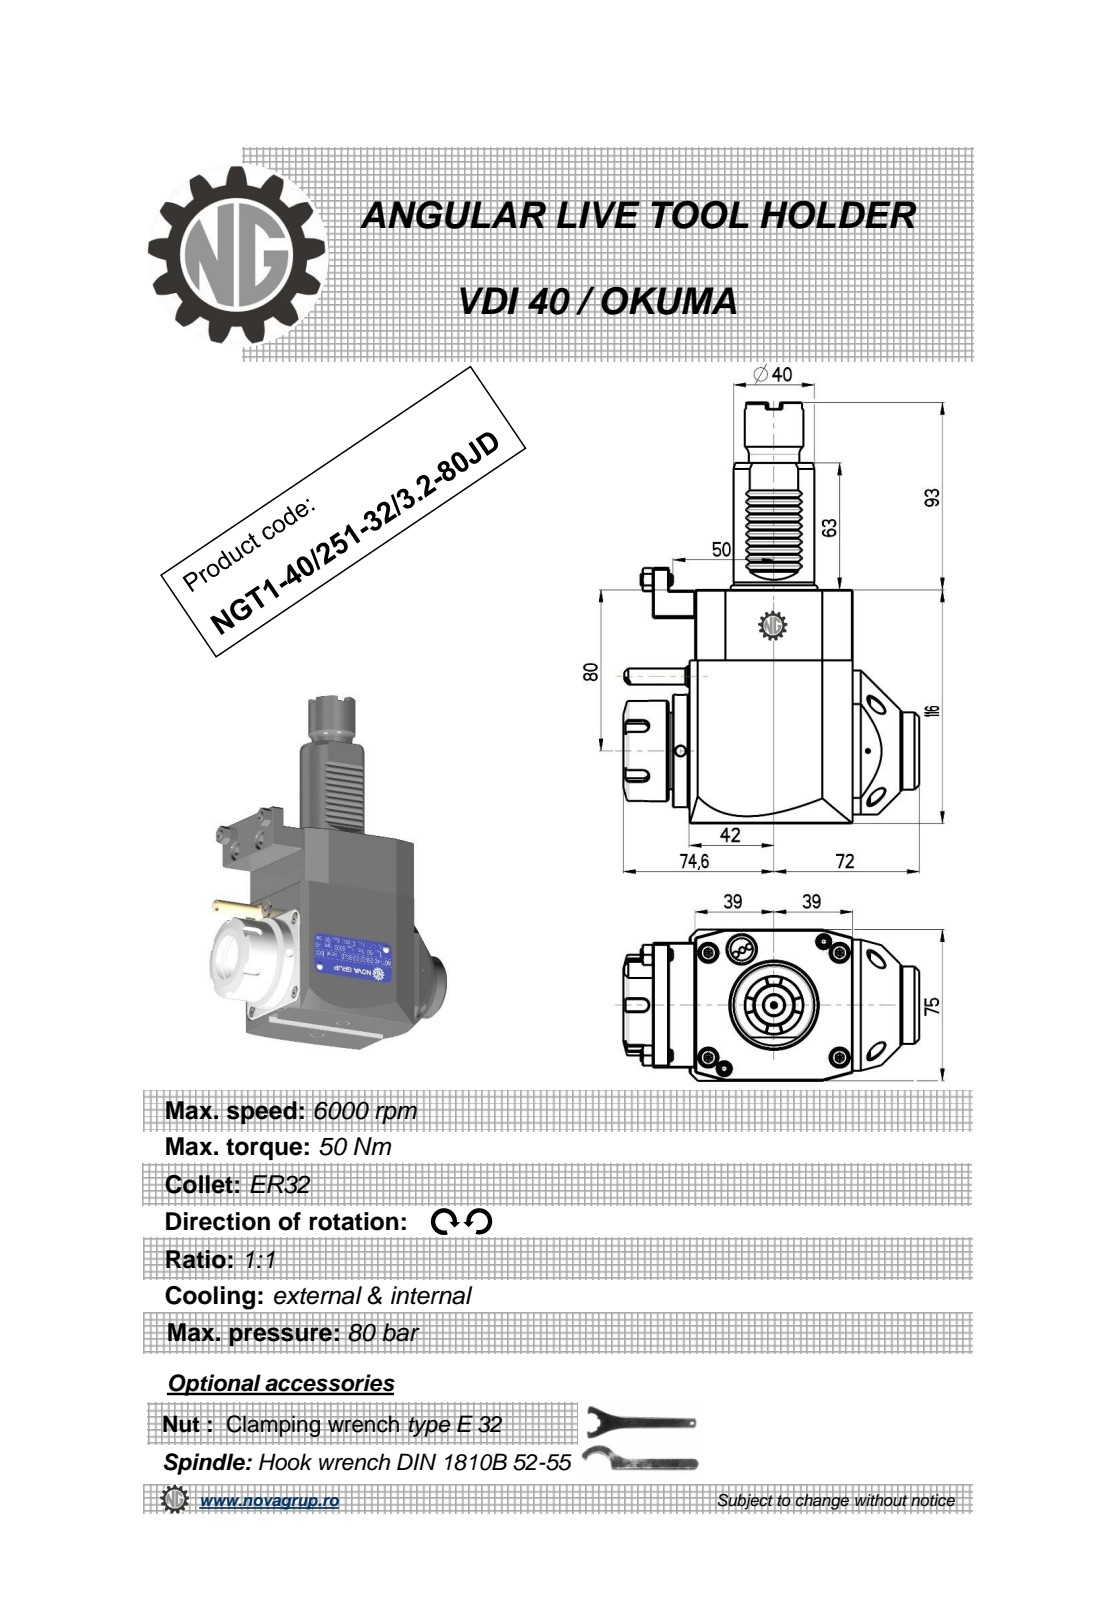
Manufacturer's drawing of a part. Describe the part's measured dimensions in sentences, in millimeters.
The part is named "NGT1_40_251_32_3_2_80JD". Its 3-D file was written by "PRO/ENGINEER BY PARAMETRIC TECHNOLOGY CORPORATION, 2010280 (CONFIG_CONTROL_DESIGN)". It is 1 solid with 456 faces: 189 planar, 83 cylindrical and 184 other. Overall it measures 209 by 146.6 by 75 millimeters. Its volume is 942 714 cubic millimeters and its surface area 77 312 square millimeters. Round holes: 3 of diameter 5, 1 of diameter 3, 1 of diameter 27. Round bosses or shafts: 2 of diameter 6, 1 of diameter 56, 1 of diameter 50, 1 of diameter 43, 1 of diameter 40, 1 of diameter 38.5, 1 of diameter 29, 1 of diameter 25. Partial cylindrical surfaces (rounded edges, fillets, slot ends): 10 of radius 0.3, 10 of radius 0.31, 6 of radius 0.2, 5 of radius 3, 1 of radius 0.5, 1 of radius 10, 1 of radius 40. The main face-to-face distances are 75, 116, 0.5, 81, 10, 21, 11, 18, 8, 80.8. The hole center spacings are 40.93.
